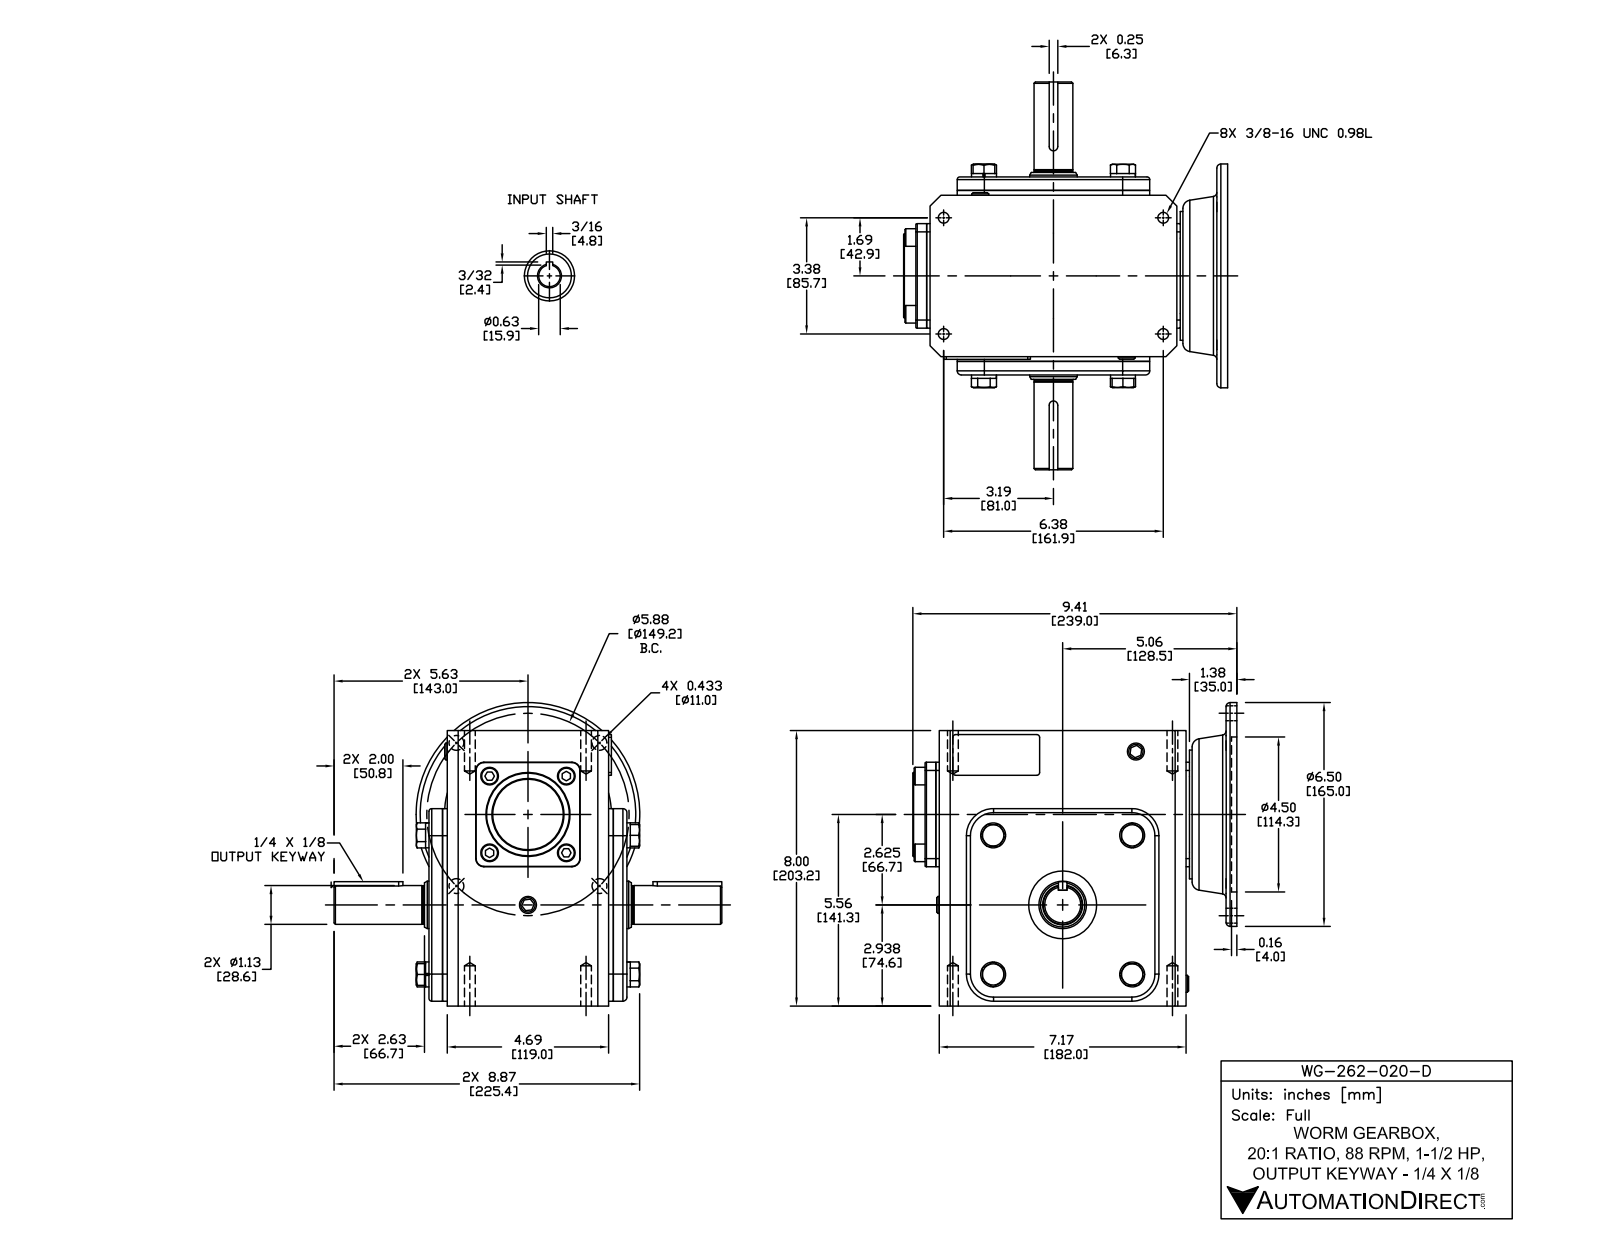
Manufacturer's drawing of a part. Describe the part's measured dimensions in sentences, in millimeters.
The part is named "WG-262-020-D". Its 3-D file was written by "SolidWorks 2015 (CONFIG_CONTROL_DESIGN)". It is 39 solids with 562 faces: 307 planar, 150 cylindrical and 105 other. Overall it measures 286 by 239 by 223.8 millimeters. Its volume is 5 278 000 cubic millimeters and its surface area 408 100 square millimeters. Round holes: 4 of diameter 8, 4 of diameter 10.3, 1 of diameter 15, 1 of diameter 15.9, 1 of diameter 30, 1 of diameter 35, 1 of diameter 37, 1 of diameter 50, 1 of diameter 97, 1 of diameter 114.3. Round bosses or shafts: 4 of diameter 18.4, 4 of diameter 13, 1 of diameter 165, 1 of diameter 62, 1 of diameter 52, 1 of diameter 29, 1 of diameter 28.6, 1 of diameter 28.3. Partial cylindrical surfaces (rounded edges, fillets, slot ends): 8 of radius 2, 8 of radius 3, 4 of radius 6, 4 of radius 20, 2 of radius 0.5, 2 of radius 1, 2 of radius 3.2. The main face-to-face distances are 126, 10, 136, 132.5, 13.5, 3.5, 122.5, 203.2, 2.5, 184.5. The hole center spacings are 74.6, 105.5, 54.6, 85.7, 130.6, 149.2, 161.9, 183.2.
